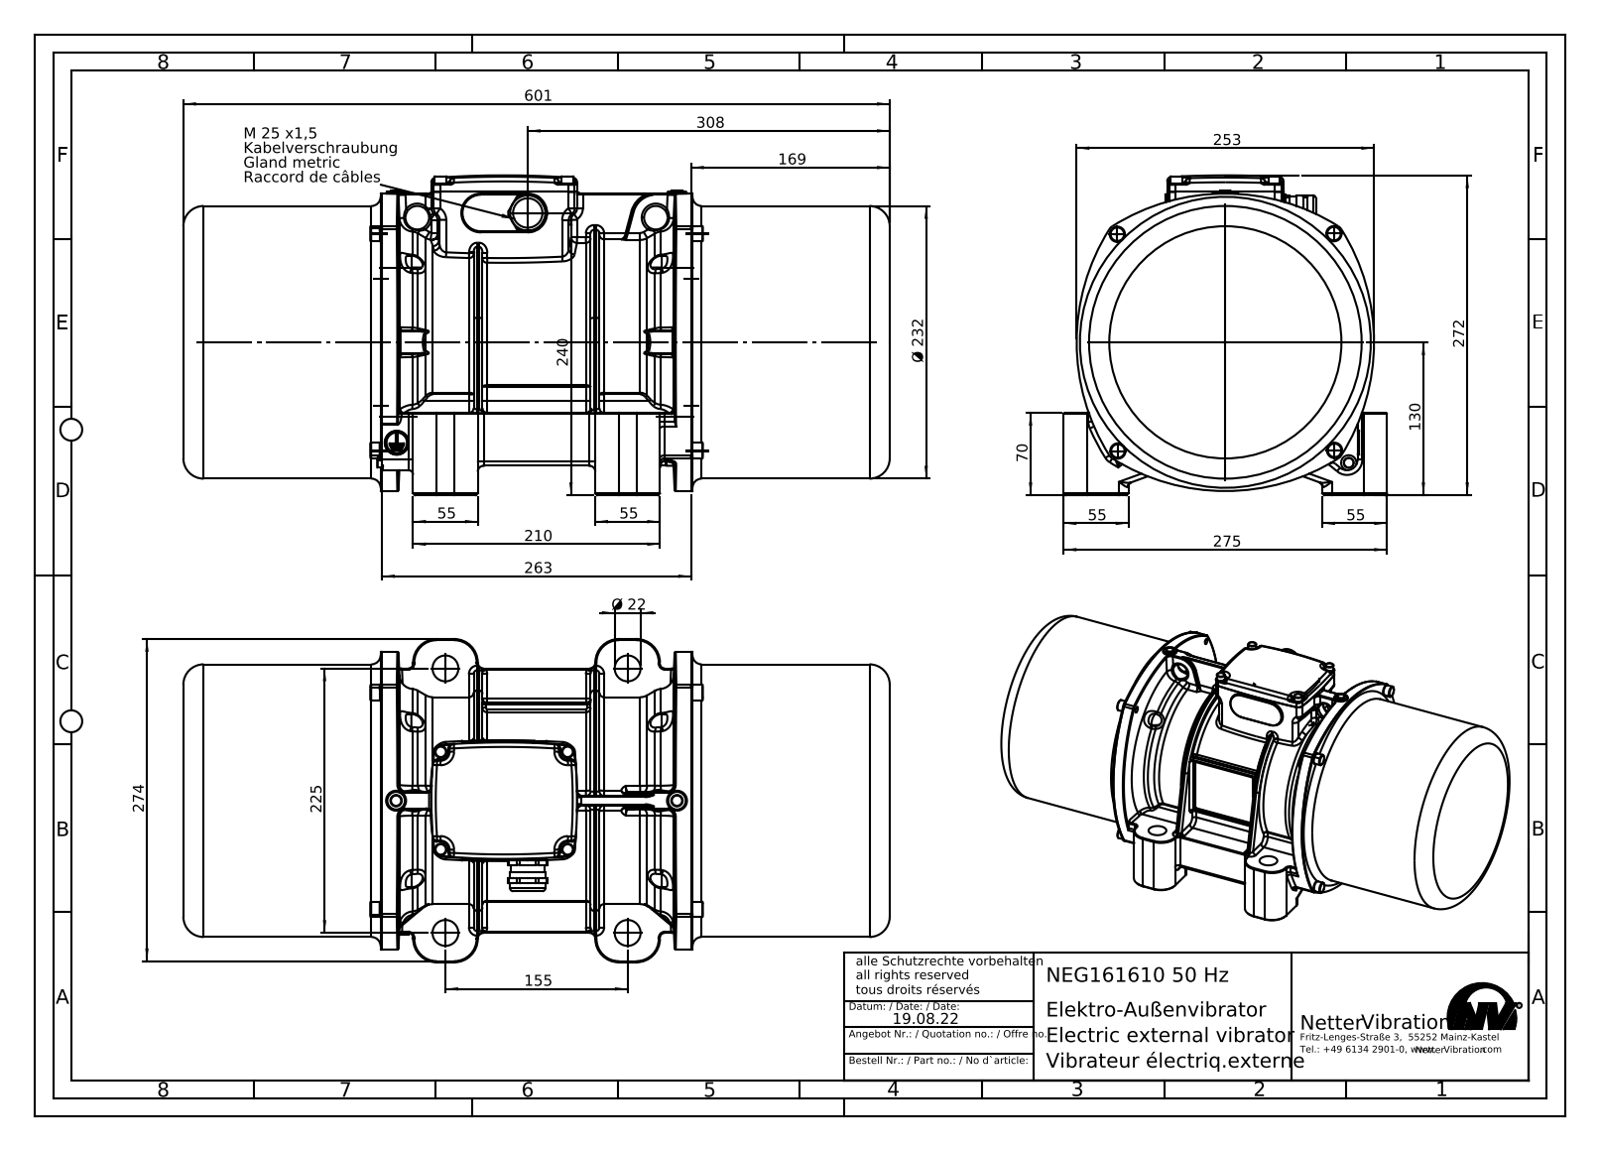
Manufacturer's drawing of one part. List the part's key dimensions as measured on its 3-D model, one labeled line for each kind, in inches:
Part name (STEP PRODUCT): NEG 161610 50Hz
STEP written by: SolidWorks 2015 (AUTOMOTIVE_DESIGN)
Units: inches
Bodies: 8 solids, 2559 faces (430 planar, 613 cylindrical, 1516 other)
Overall size (bounding box): 23.661 × 10.827 × 10.709
Volume: 1 390 in³ · Surface area: 2 007 in²
Round holes (diameter × count): ⌀0.866 ×4, ⌀0.787 ×2, ⌀0.512 ×1, ⌀0.709 ×1, ⌀0.984 ×1, ⌀5.984 ×1, ⌀8.268 ×1, ⌀9.567 ×1
Round bosses / shafts (diameter × count): ⌀0.394 ×8, ⌀0.63 ×4, ⌀0.512 ×4, ⌀0.236 ×4, ⌀0.383 ×2, ⌀9.13 ×1, ⌀6.496 ×1, ⌀5.512 ×1
Partial cylindrical surfaces — rounded edges, fillets, slot ends (radius × count): R0.008 ×102, R0.157 ×57, R0.197 ×56, R0.039 ×24, R0.118 ×20, R0.315 ×17, R0.079 ×14, R0.394 ×10
Main face-to-face distances: 6.654, 17.008, 0.138, 6.791, 16.87, 10.217, 7.5, 0.709, 16.161, 0.846
Hole centre spacings: 5.378, 6.102, 8.858, 10.757, 0.794, 4.603, 5.306, 5.564
